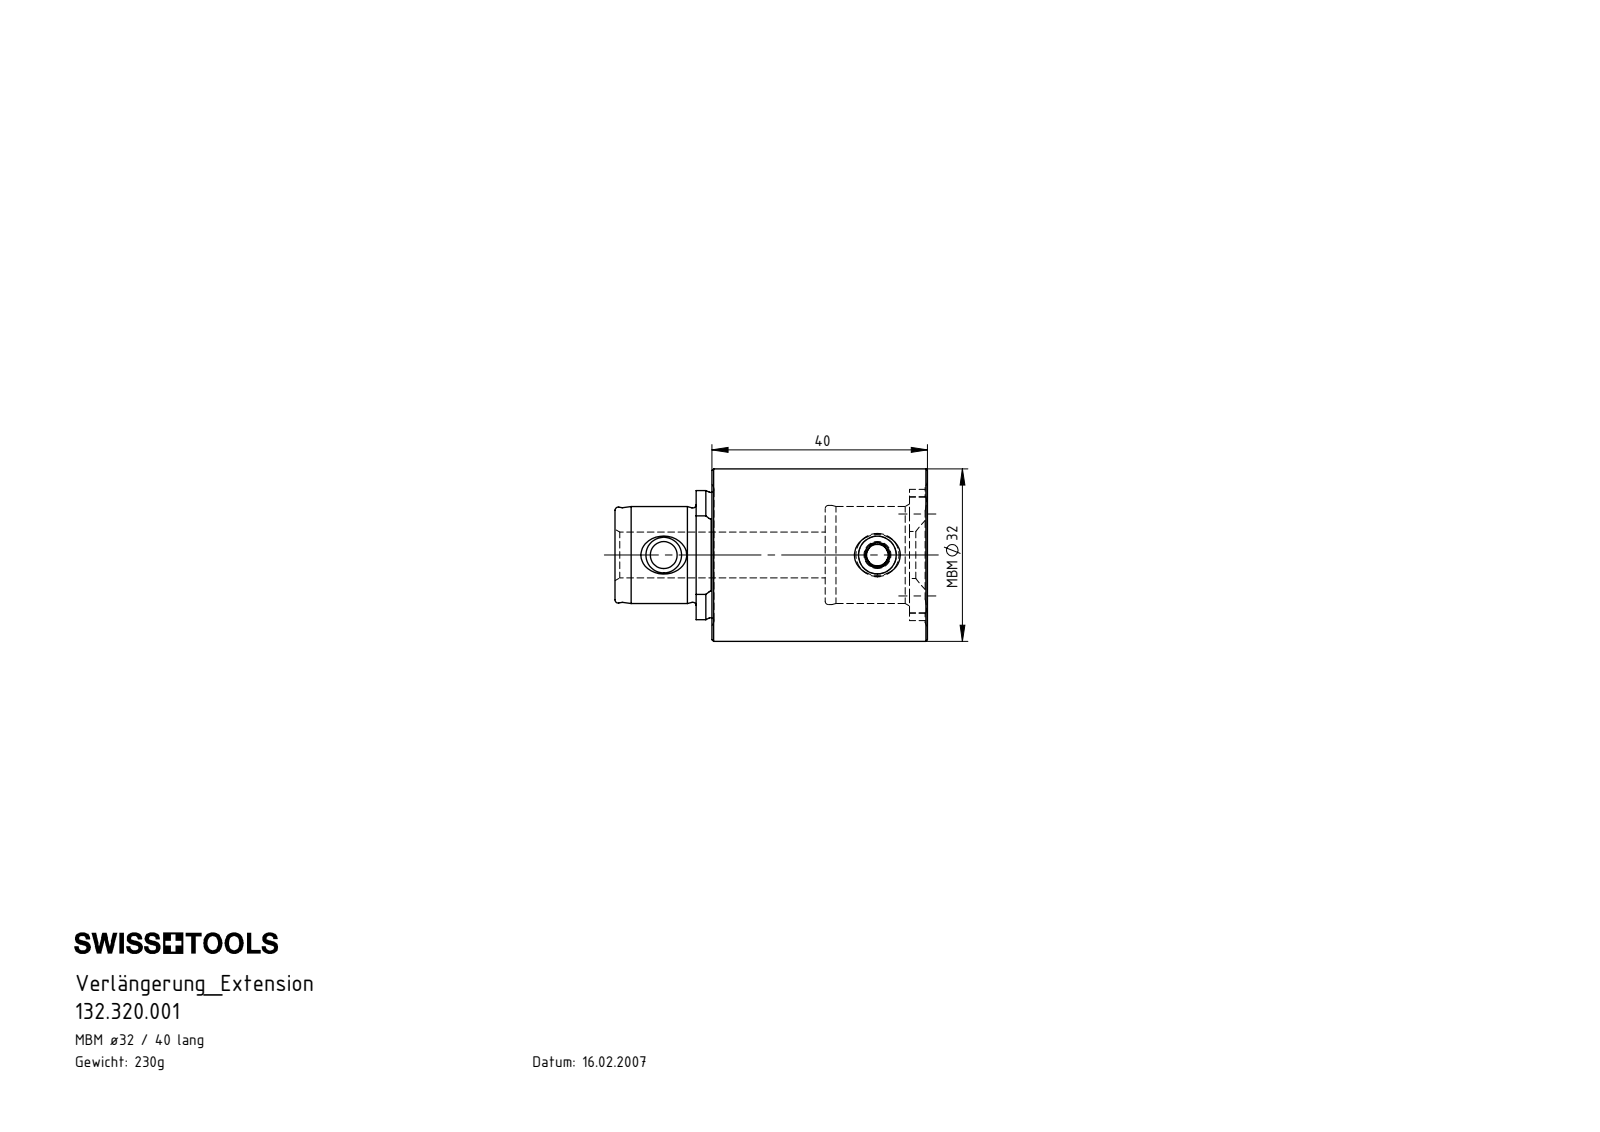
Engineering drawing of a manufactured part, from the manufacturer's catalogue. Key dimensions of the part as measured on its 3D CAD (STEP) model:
Part name (STEP PRODUCT): MB3.MB3.K01.040; MB3-MB3-K01.040_B; MB3-ER1.001.011_A
STEP written by: SolidWorks 2012 (CONFIG_CONTROL_DESIGN)
Units: millimetres
Bodies: 2 solids, 117 faces (26 planar, 30 cylindrical, 61 other)
Overall size (bounding box): 58 × 32 × 32
Volume: 29 305 mm³ · Surface area: 9 146 mm²
Round holes (diameter × count): ⌀5 ×1, ⌀7 ×1, ⌀8.5 ×1, ⌀18 ×1, ⌀18.4 ×1
Round bosses / shafts (diameter × count): ⌀32 ×1, ⌀8 ×1
Partial cylindrical surfaces — rounded edges, fillets, slot ends (radius × count): R3.2 ×4, R10.5 ×1, R11.97 ×1, R12.18 ×1
Main face-to-face distances: 19, 40, 21, 36.65, 15.65, 3.35, 18, 39, 54.65, 58
Hole centre spacings: 39.65
